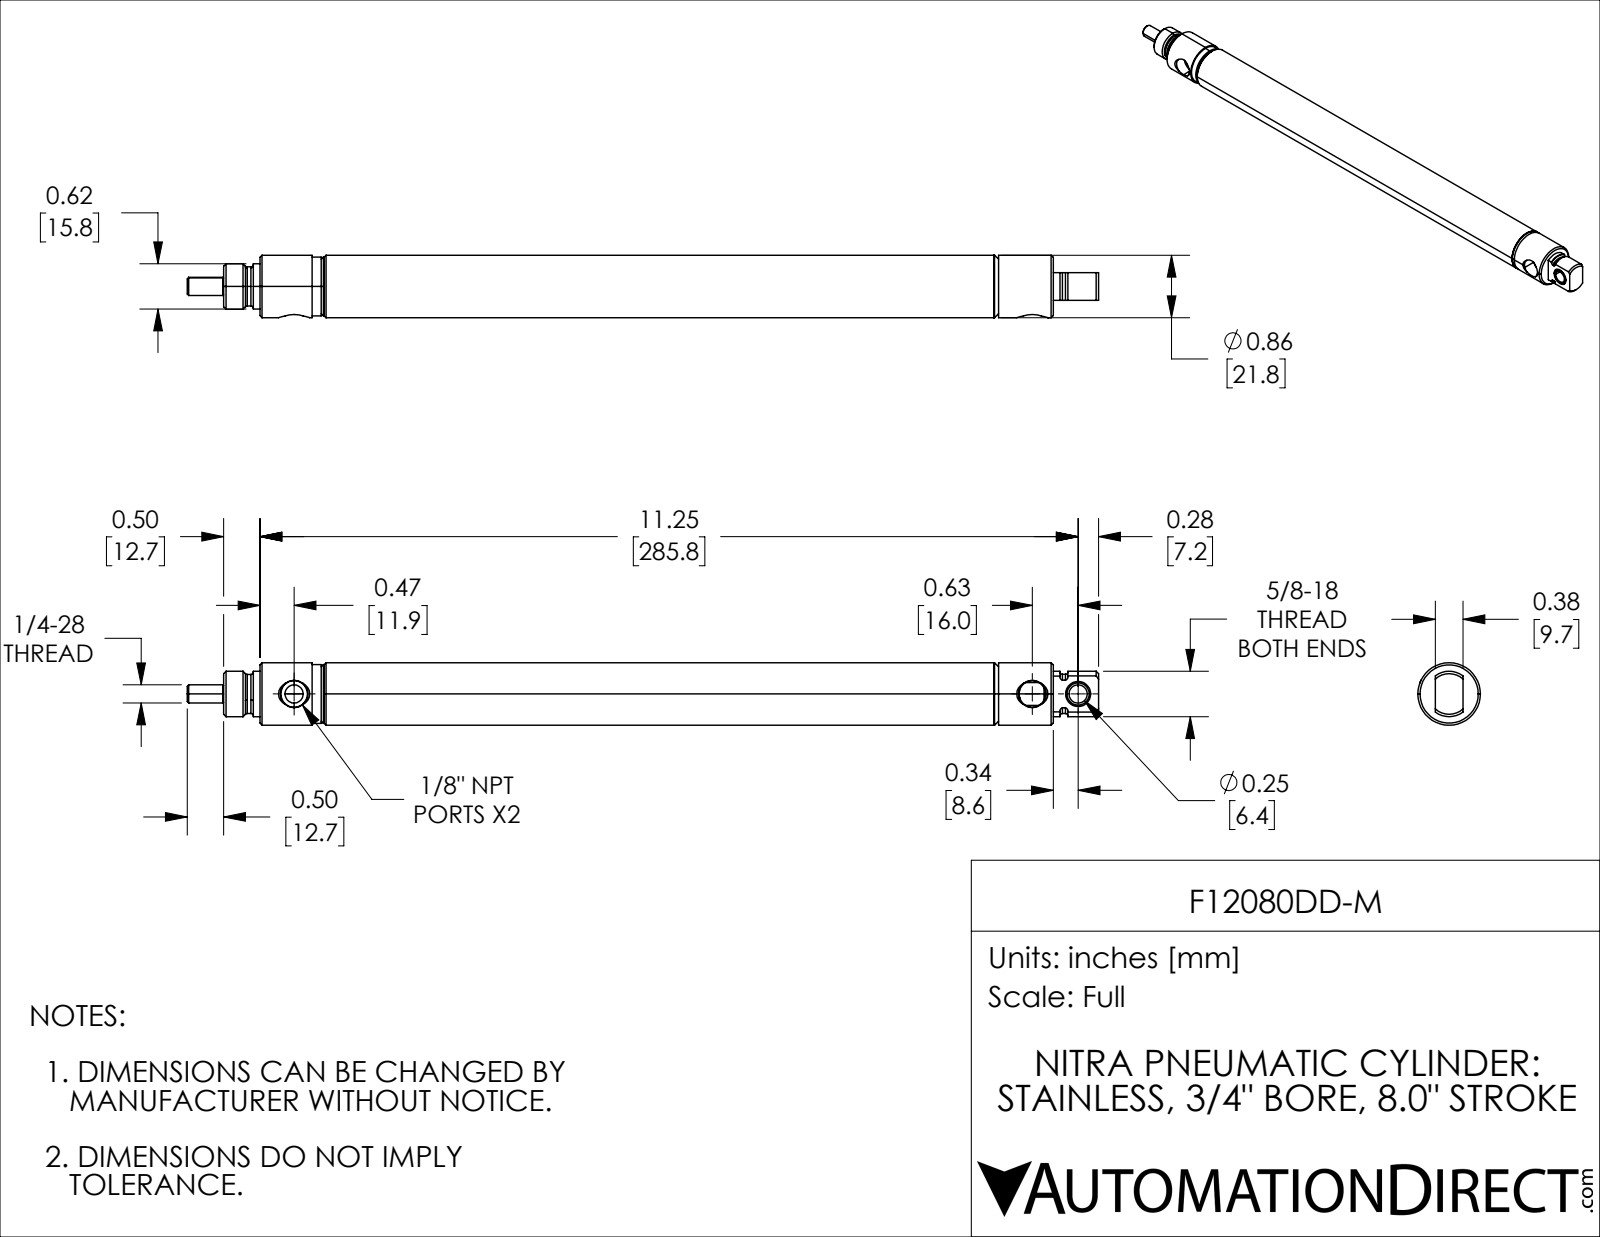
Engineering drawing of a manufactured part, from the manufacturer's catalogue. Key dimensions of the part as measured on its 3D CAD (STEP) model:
Part name (STEP PRODUCT): F12080DD-M_7; F12080DD-M_5; F12080DD-M_9; F12080DD-M_3 (+2 more)
STEP written by: SolidWorks 2021 (CONFIG_CONTROL_DESIGN)
Units: millimetres
Bodies: 5 solids, 158 faces (29 planar, 61 cylindrical, 68 other)
Overall size (bounding box): 318.31 × 21.84 × 21.84
Volume: 52 087 mm³ · Surface area: 46 790 mm²
Round holes (diameter × count): ⌀6.35 ×1, ⌀6.38 ×1, ⌀6.95 ×1, ⌀7.92 ×1, ⌀8.78 ×1, ⌀9.23 ×1, ⌀12.7 ×1, ⌀17.83 ×1
Round bosses / shafts (diameter × count): ⌀21.84 ×1, ⌀20.57 ×1, ⌀19.35 ×1, ⌀15.88 ×1, ⌀15.81 ×1, ⌀13.68 ×1, ⌀6.35 ×1, ⌀5.84 ×1
Partial cylindrical surfaces — rounded edges, fillets, slot ends (radius × count): R6.84 ×1
Main face-to-face distances: 21.43, 40.49, 265.12, 203.2, 224.63, 249.32, 46.12, 24.69, 12.7, 9.66
Hole centre spacings: 16, 257.81, 273.81
